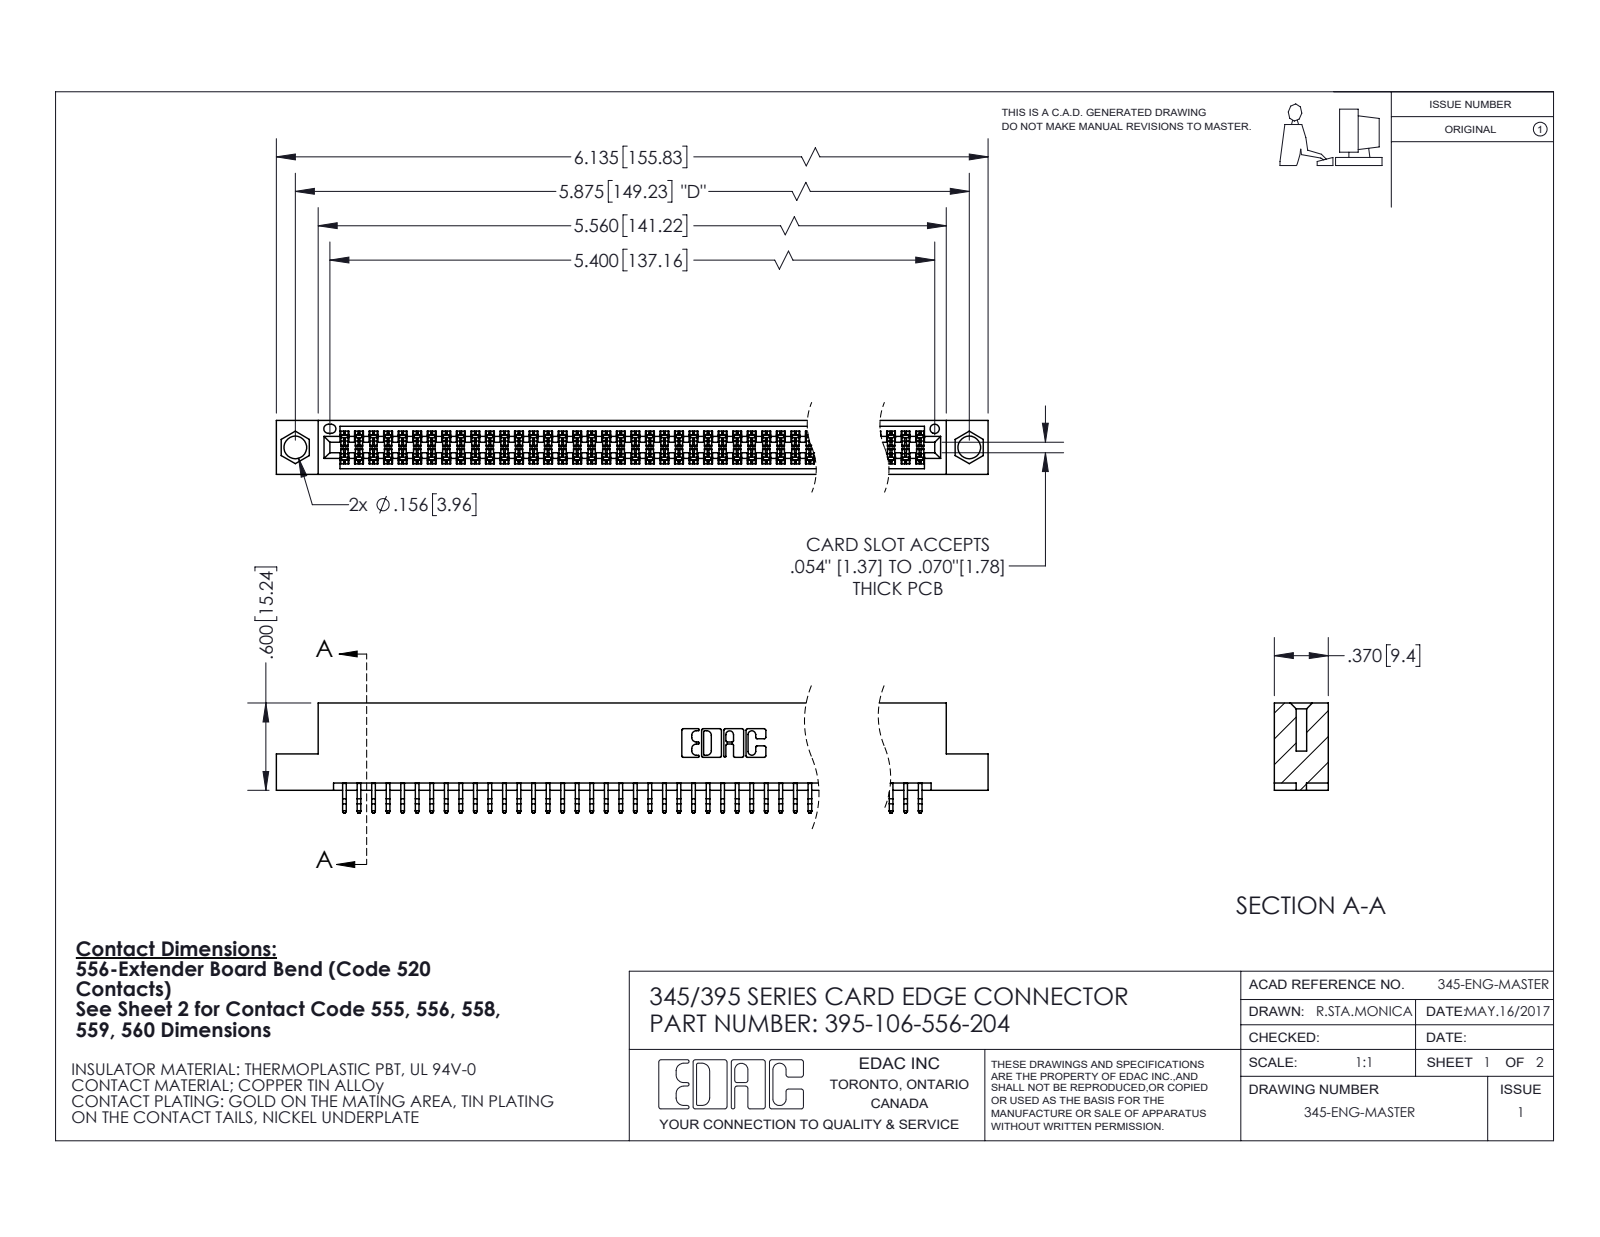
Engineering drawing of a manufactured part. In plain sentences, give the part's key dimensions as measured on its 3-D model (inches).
The part is named "395-106-556-204; 345 Part_Flush Mounting Lugs - 0.156 Dia-TI; 345-292-001_556 Tail". Its 3-D file was written by "SolidWorks 2020 (CONFIG_CONTROL_DESIGN)". It is 107 solids with 6076 faces: 4016 planar, 2060 cylindrical and 0 other. Overall it measures 6.135 by 0.757 by 0.37 inches. Its volume is 0.923 cubic inches and its surface area 34.62 square inches. Round holes: 2 of diameter 0.156, 1 of diameter 0.064. Partial cylindrical surfaces (rounded edges, fillets, slot ends): 212 of radius 0.006, 22 of radius 0.01, 6 of radius 0.007, 6 of radius 0.031, 3 of radius 0.026, 2 of radius 0.01, 2 of radius 0.014, 2 of radius 0.019. The main face-to-face distances are 0.298, 0.072, 0.37, 0.2, 0.025, 0.098, 0.272, 0.225, 0.175, 0.149. The hole center spacings are 0.27, 5.639, 5.875.
